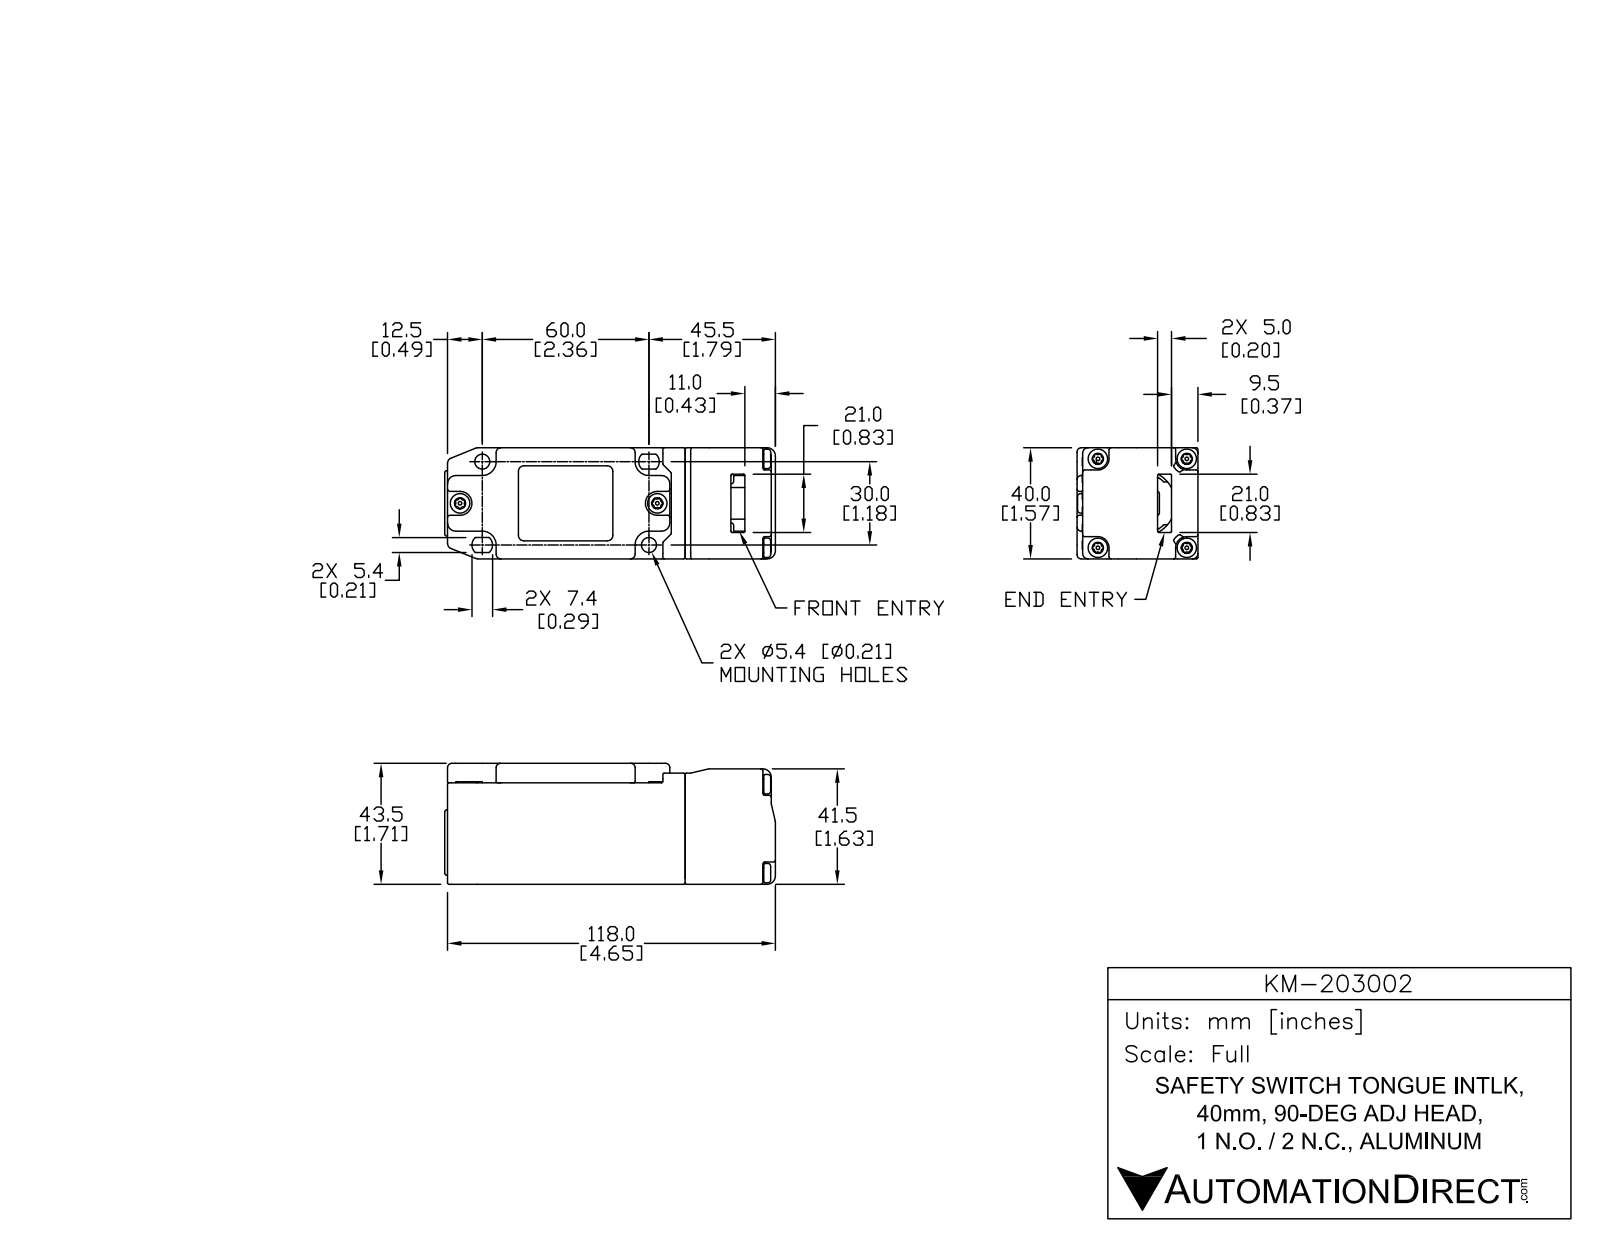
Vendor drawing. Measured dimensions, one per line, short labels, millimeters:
name: KM-203002
written by: SolidWorks 2013 (AUTOMOTIVE_DESIGN)
unit: mm
bodies: 1 solid, 581 faces (128 planar, 263 cylindrical, 190 other)
size: 119.63 × 43.56 × 40
volume: 183 300 mm³; area: 28 465 mm²
holes: 2× ⌀5.4
bosses: 4× ⌀6.77, 2× ⌀6.63, 1× ⌀23, 1× ⌀5.6
rounds: 95× R0.5, 68× R0.25, 5× R3, 4× R1.45, 4× R1.7, 4× R2.75, 4× R4, 4× R5
face distances: 40, 43.5, 0.5, 43, 118, 2.6, 5, 9.5, 102, 16
hole spacings: 67.08
